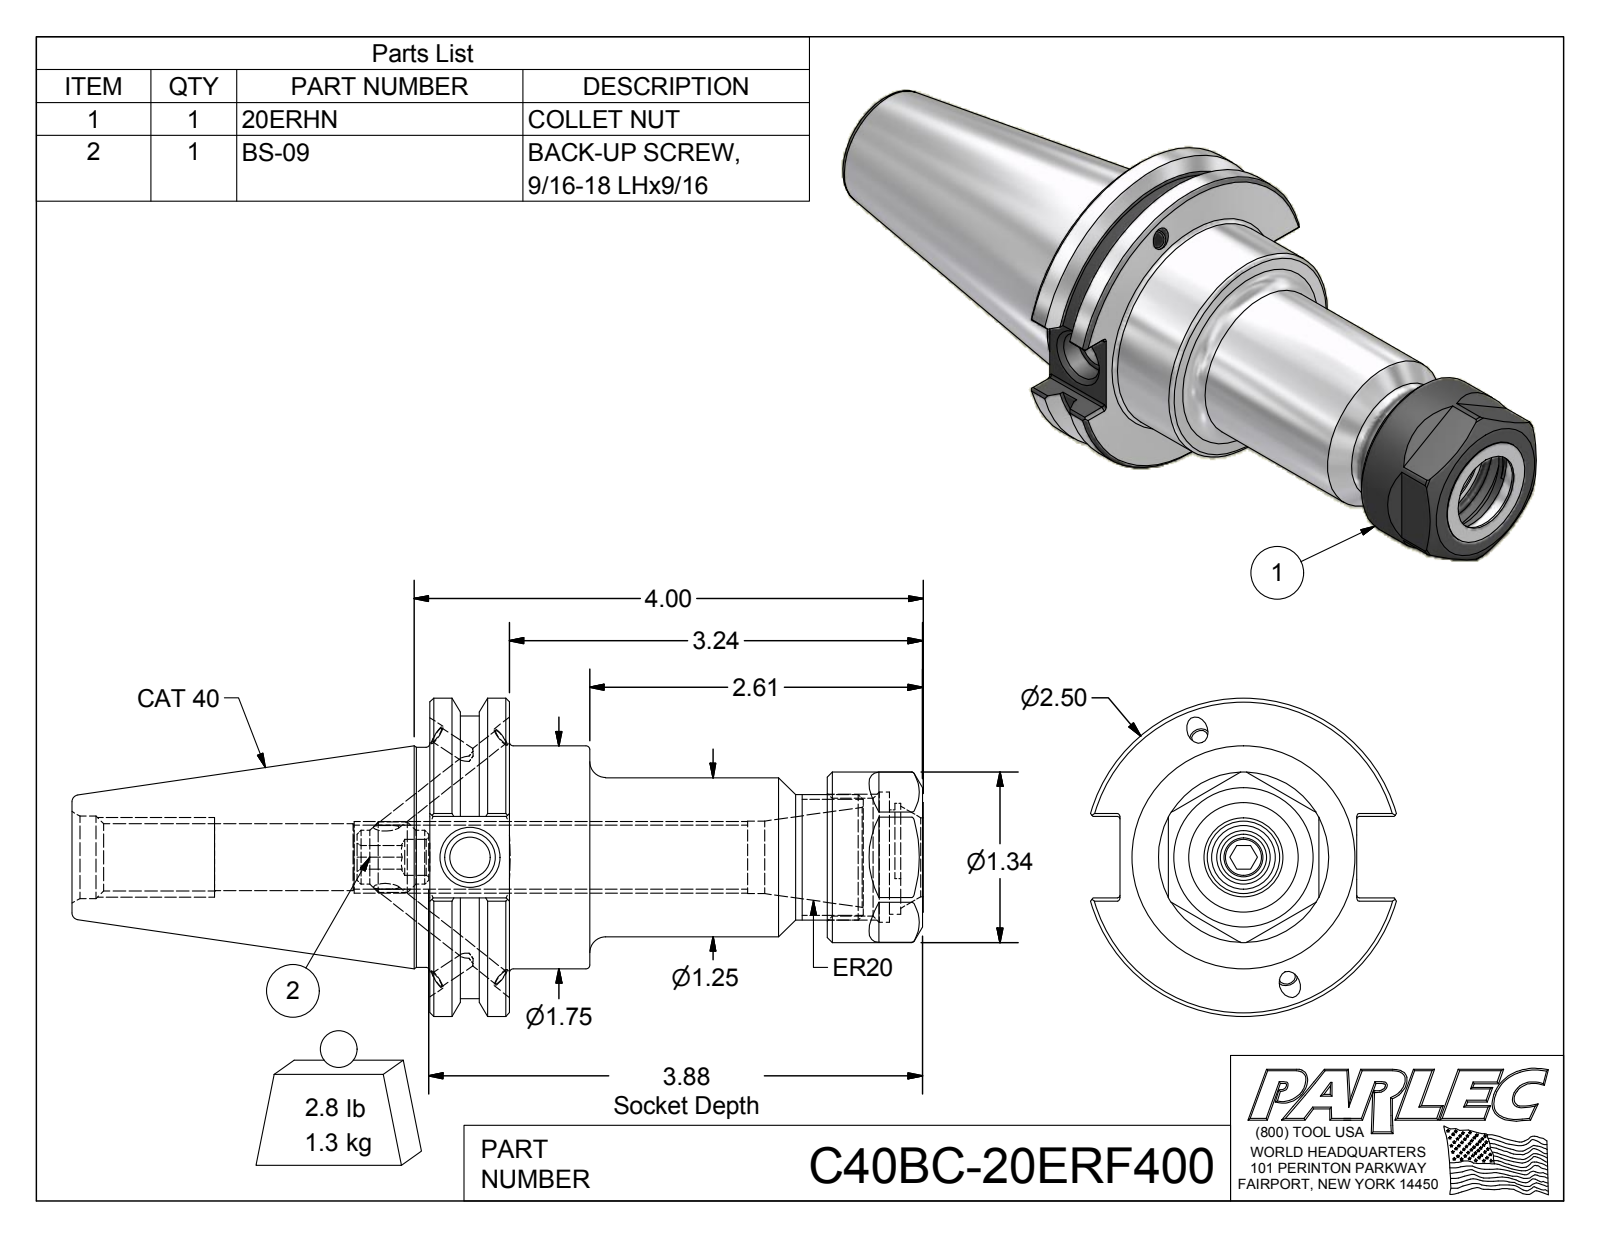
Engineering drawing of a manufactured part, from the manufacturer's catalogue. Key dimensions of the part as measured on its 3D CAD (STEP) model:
Part name (STEP PRODUCT): C40BC-20ER4-1; 029-965; C40BCB-20ER4-1; BS-09 (+2 more)
STEP written by: Autodesk Inventor 2016 (AUTOMOTIVE_DESIGN)
Units: millimetres
Bodies: 7 solids, 226 faces (108 planar, 60 cylindrical, 58 other)
Overall size (bounding box): 169.86 × 63.5 × 61.05
Volume: 162 346 mm³ · Surface area: 36 867 mm²
Round holes (diameter × count): ⌀3.3 ×4, ⌀4.1 ×4, ⌀7.14 ×1, ⌀8 ×1, ⌀10.13 ×1, ⌀12.75 ×1, ⌀13.36 ×1, ⌀13.39 ×1, ⌀14.48 ×1, ⌀15.49 ×1, ⌀16.46 ×1, ⌀23.5 ×1
Round bosses / shafts (diameter × count): ⌀4.2 ×4, ⌀4 ×4, ⌀63.5 ×1, ⌀56.36 ×1, ⌀44.45 ×1, ⌀43.94 ×1, ⌀34 ×1, ⌀31.75 ×1
Partial cylindrical surfaces — rounded edges, fillets, slot ends (radius × count): R0.51 ×12, R9.47 ×1, R10.55 ×1, R10.75 ×1
Main face-to-face distances: 15.87, 98.42, 82.55, 30, 16, 31.87, 66.55, 79.35, 63.48, 47.48
